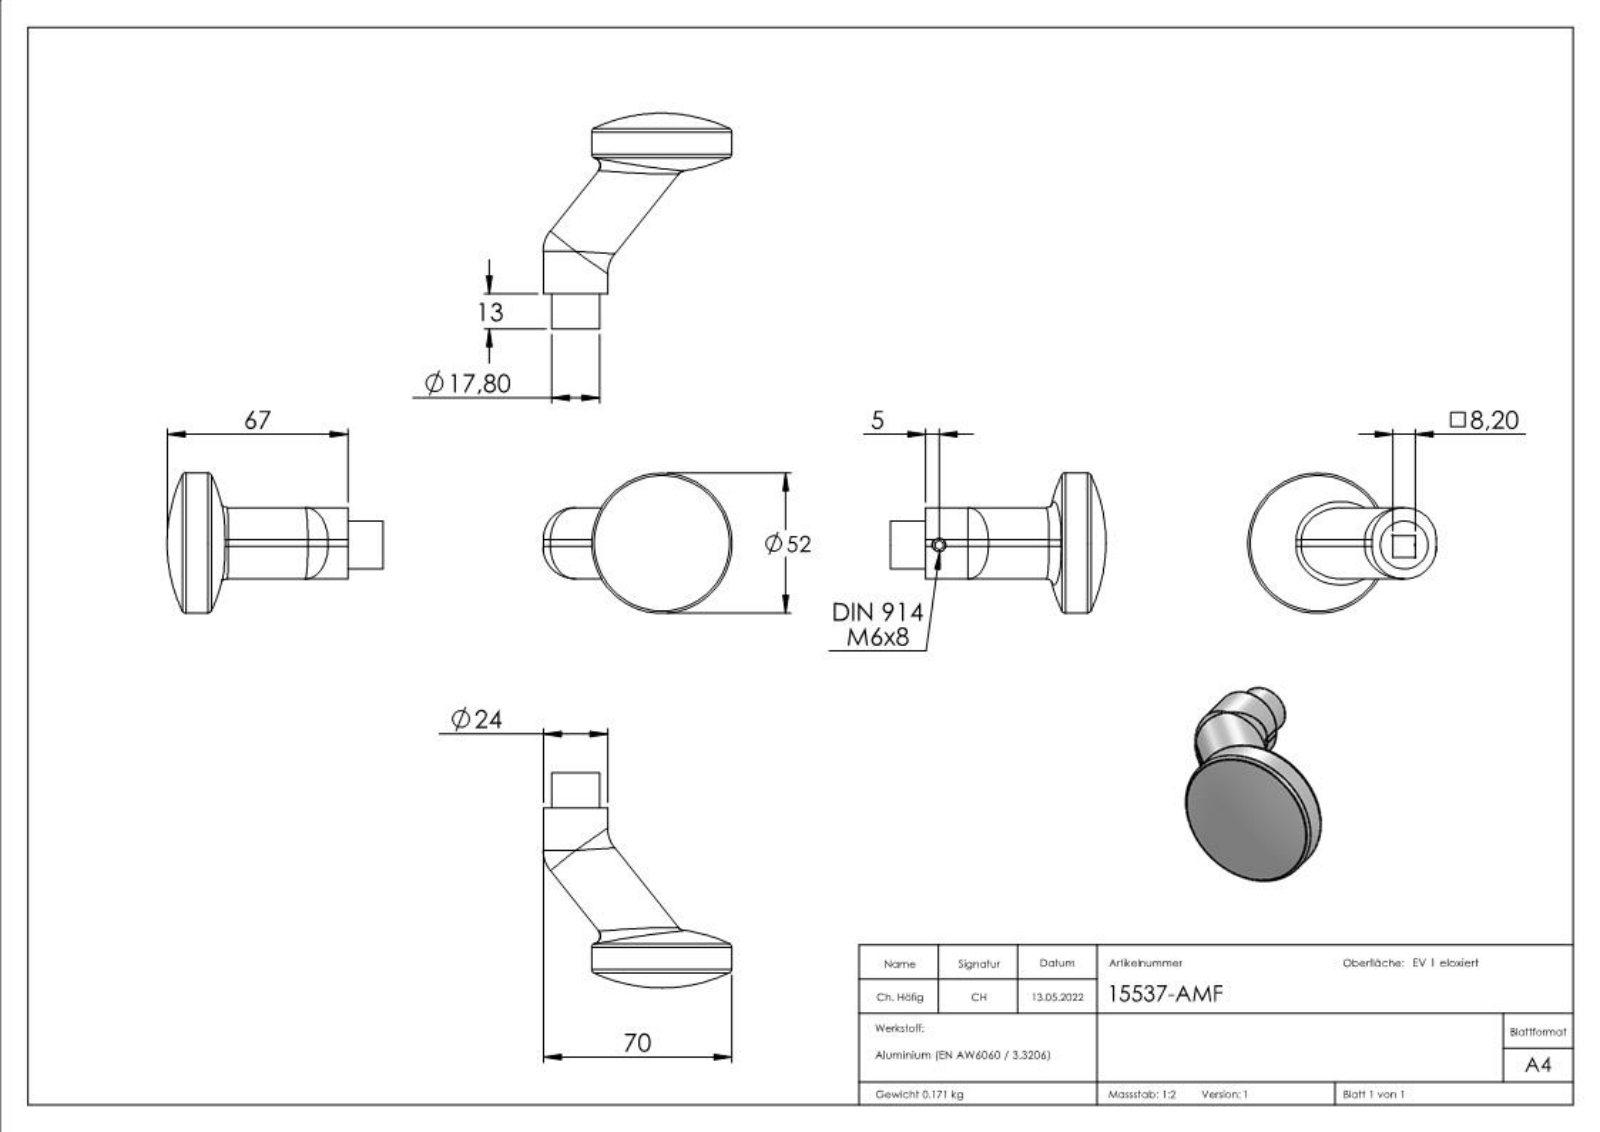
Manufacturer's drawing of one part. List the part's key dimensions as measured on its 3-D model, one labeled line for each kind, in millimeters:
Part name (STEP PRODUCT): 15537-AMF; 15537-AMF Teil1_15537-AMF Teil1; DIN914_DIN 914 M6x8
STEP written by: SolidWorks 2018 (CONFIG_CONTROL_DESIGN)
Units: millimetres
Bodies: 2 solids, 267 faces (161 planar, 14 cylindrical, 92 other)
Overall size (bounding box): 80 × 70 × 52
Volume: 63 090 mm³ · Surface area: 12 667 mm²
Round holes (diameter × count): ⌀5 ×1
Round bosses / shafts (diameter × count): ⌀52 ×1, ⌀17.8 ×1, ⌀6 ×1
Partial cylindrical surfaces — rounded edges, fillets, slot ends (radius × count): R12 ×6, R0.25 ×4
Main face-to-face distances: 8.2, 13, 24, 23.99, 37, 7.9, 16.1, 3, 3.5, 20.5
